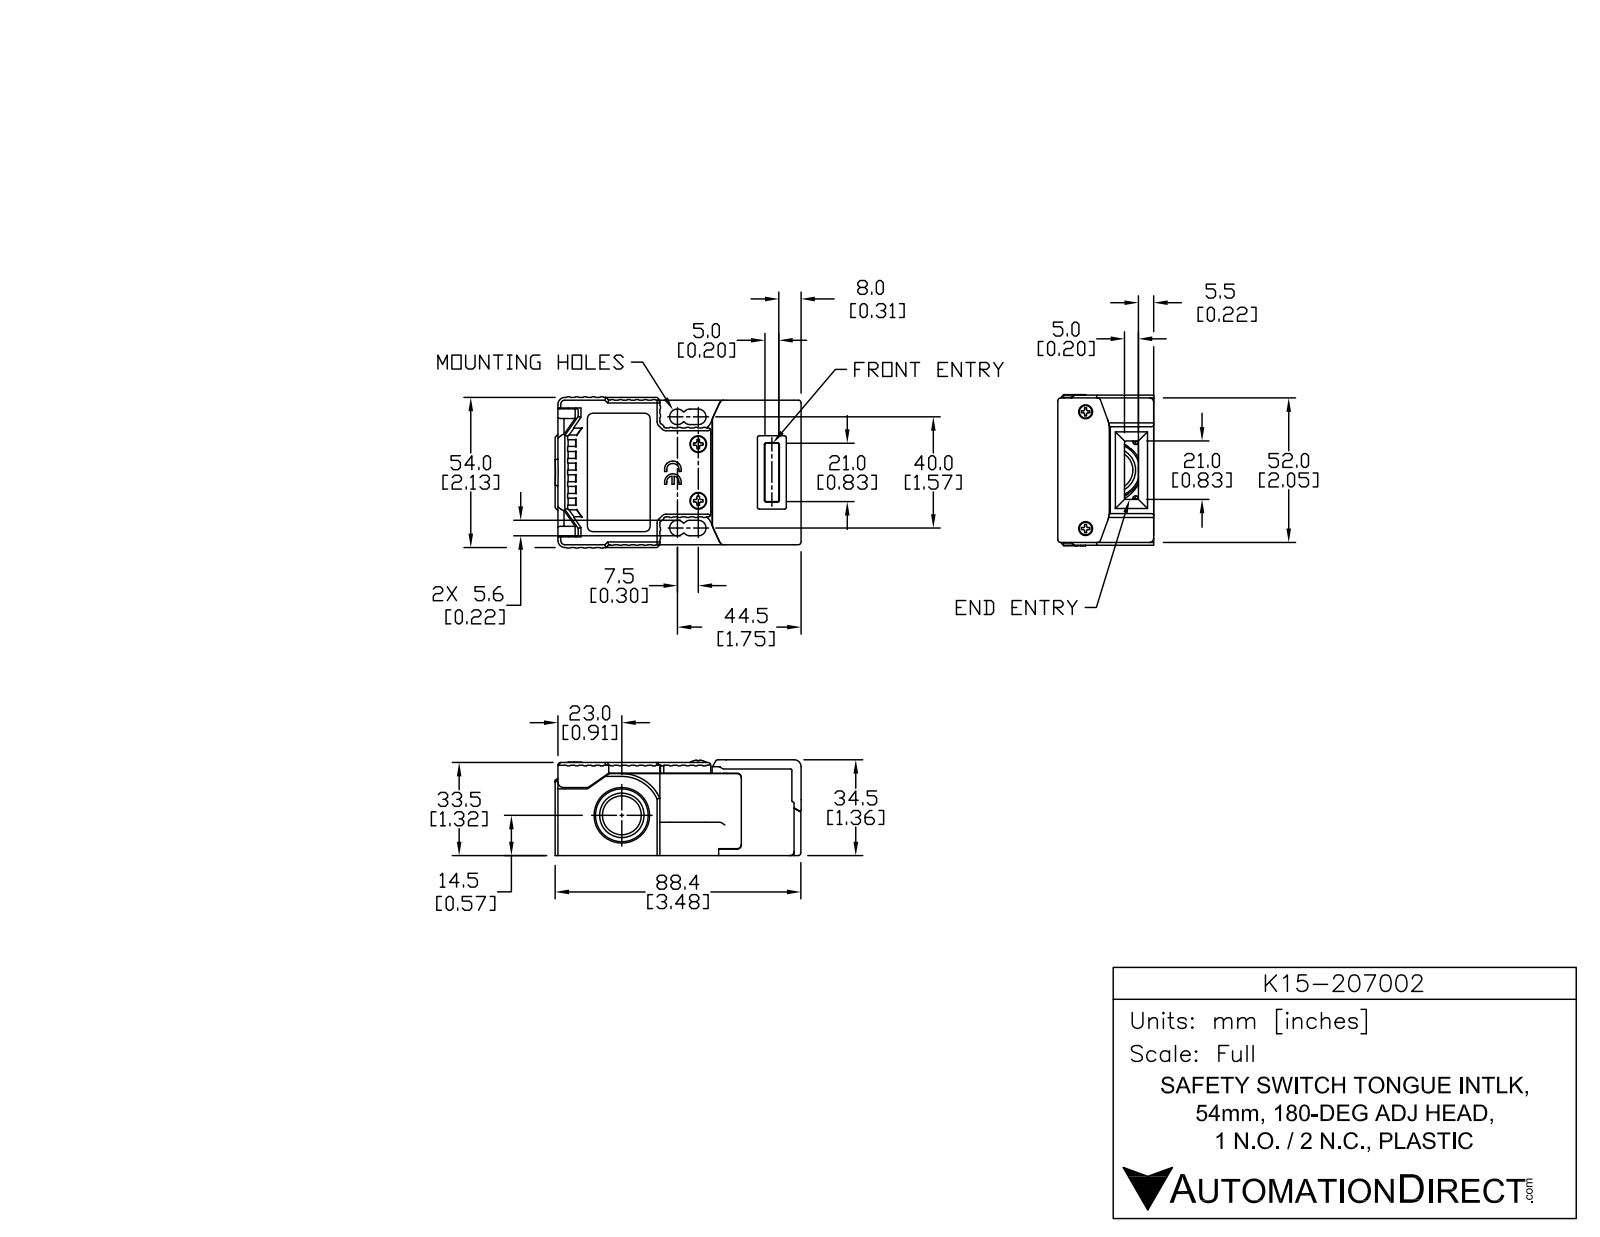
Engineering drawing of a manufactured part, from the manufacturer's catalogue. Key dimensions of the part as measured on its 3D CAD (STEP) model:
Part name (STEP PRODUCT): K-15-207002
STEP written by: SolidWorks 2013 (AUTOMOTIVE_DESIGN)
Units: millimetres
Bodies: 1 solid, 376 faces (166 planar, 137 cylindrical, 73 other)
Overall size (bounding box): 89.5 × 58 × 34.6
Volume: 143 347 mm³ · Surface area: 23 178 mm²
Round holes (diameter × count): ⌀19.33 ×1, ⌀20 ×1
Round bosses / shafts (diameter × count): ⌀4.5 ×2
Partial cylindrical surfaces — rounded edges, fillets, slot ends (radius × count): R0.5 ×94, R2.8 ×6, R3 ×4, R4 ×3
Main face-to-face distances: 3, 55, 33.5, 1, 52, 34.5, 33.45, 1.05, 87.4, 12.8
